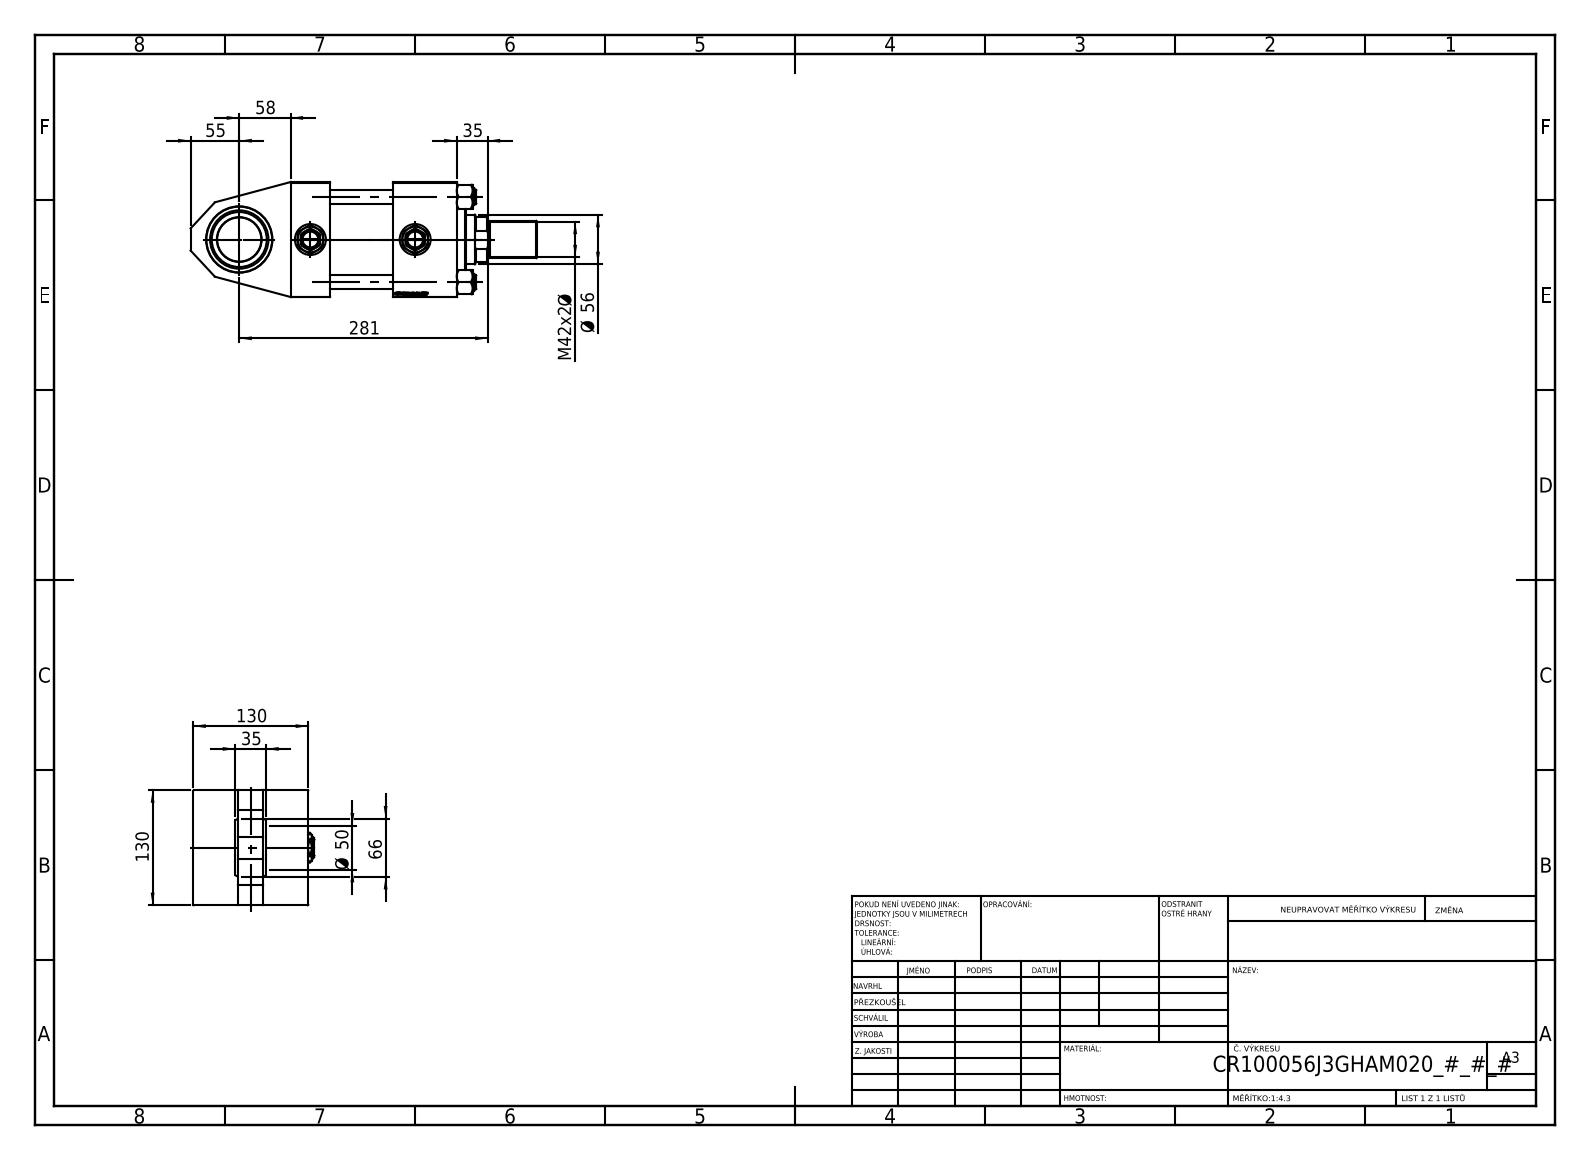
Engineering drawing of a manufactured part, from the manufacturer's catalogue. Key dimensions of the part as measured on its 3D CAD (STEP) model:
Part name (STEP PRODUCT): ROD_END_AH; V215CR_J_VNITRNI_KROUZEK; V215CR_TYCINKA_J; V215CR_J_Body (+4 more)
STEP written by: SolidWorks 2019 (CONFIG_CONTROL_DESIGN)
Units: millimetres
Bodies: 15 solids, 1308 faces (616 planar, 104 cylindrical, 588 other)
Overall size (bounding box): 392 × 137 × 130
Volume: 2 814 000 mm³ · Surface area: 396 665 mm²
Round holes (diameter × count): ⌀16 ×4, ⌀2.5 ×2, ⌀7 ×2, ⌀26.44 ×2, ⌀35 ×2, ⌀40.5 ×1, ⌀50 ×1, ⌀56 ×1, ⌀59 ×1, ⌀75 ×1, ⌀76 ×1, ⌀85.5 ×1
Round bosses / shafts (diameter × count): ⌀19 ×4, ⌀106 ×1, ⌀72 ×1, ⌀42 ×1, ⌀40 ×1
Partial cylindrical surfaces — rounded edges, fillets, slot ends (radius × count): R27 ×1
Main face-to-face distances: 130, 51, 79, 45, 188, 143, 71, 116, 72, 28
Hole centre spacings: 49.02, 68.52, 96.9, 101.73, 41, 137.04, 80.5, 82
